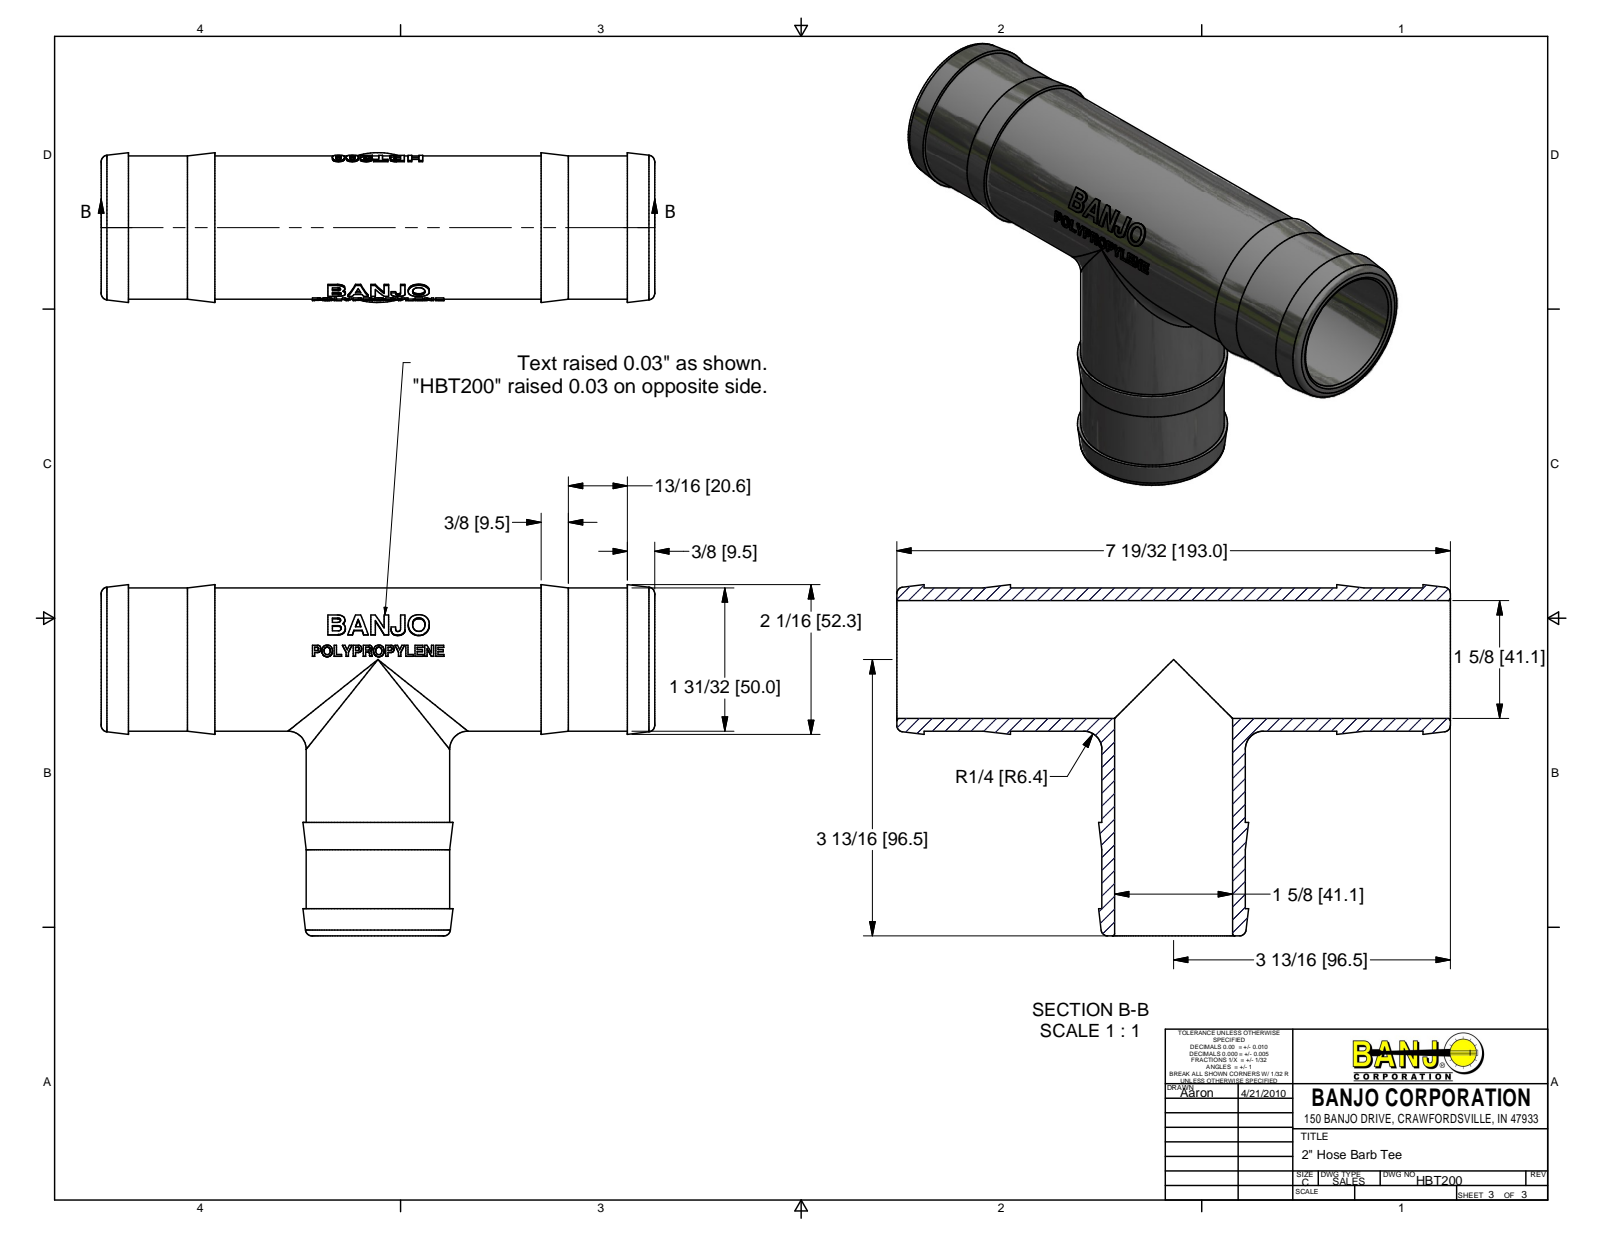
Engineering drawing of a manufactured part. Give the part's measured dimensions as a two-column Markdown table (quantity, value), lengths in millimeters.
| quantity | value |
| --- | --- |
| part name | HBT200 |
| STEP written by | Autodesk Inventor 2016 (AUTOMOTIVE_DESIGN) |
| units | millimeters |
| bodies | 1 solid, 360 faces (159 planar, 45 cylindrical, 156 other) |
| overall size | 193.04 × 122.68 × 52.32 |
| volume | 171 291 mm³ |
| surface area | 77 526 mm² |
| round holes (diameter × count) | 41.15 × 2 |
| round bosses / shafts (diameter × count) | 50.04 × 2 |
| partial cylindrical surfaces (radius × count) | 25.53 × 1 |
| main face-to-face distances | 9.53, 39.62, 30.09, 153.42, 183.51, 143.89, 193.04, 173.98, 113.8, 1.57 |
